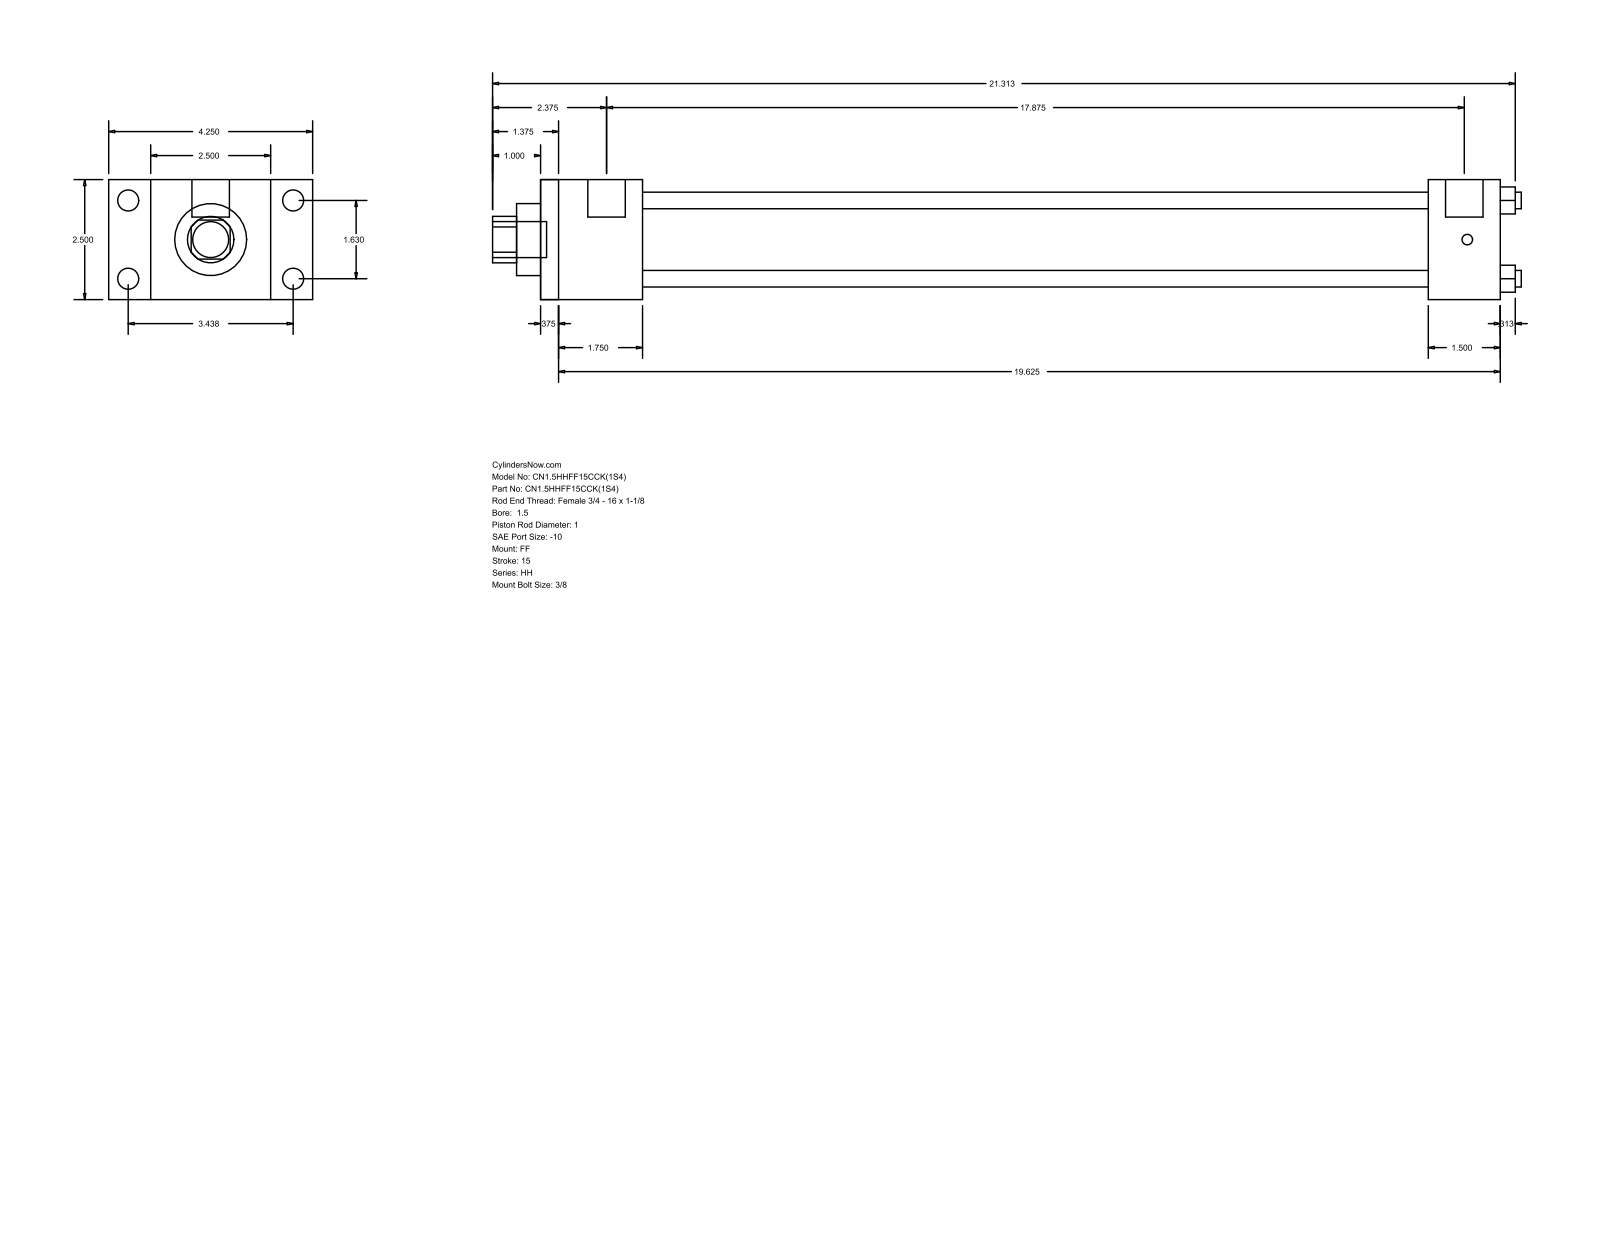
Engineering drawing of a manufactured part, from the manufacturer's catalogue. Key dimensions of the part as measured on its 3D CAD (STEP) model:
Part name (STEP PRODUCT): HH_FF__0150_1
STEP written by: GSSL Pune (CONFIG_CONTROL_DESIGN)
Units: millimetres
Bodies: 0 solids, 92 faces (64 planar, 28 cylindrical, 0 other)
Overall size (bounding box): 544.51 × 107.95 × 63.5
Round holes (diameter × count): ⌀8.76 ×4, ⌀25.4 ×1, ⌀38.1 ×1, ⌀44.45 ×1
Round bosses / shafts (diameter × count): ⌀11.13 ×4, ⌀5.56 ×4, ⌀19.84 ×2, ⌀19.05 ×1
Partial cylindrical surfaces — rounded edges, fillets, slot ends (radius × count): R12.29 ×1
Main face-to-face distances: 63.5, 508, 9.52, 498.48, 53.98, 44.46, 454.02, 469.9, 460.38, 415.92
Hole centre spacings: 29.27, 41.4, 58.55
